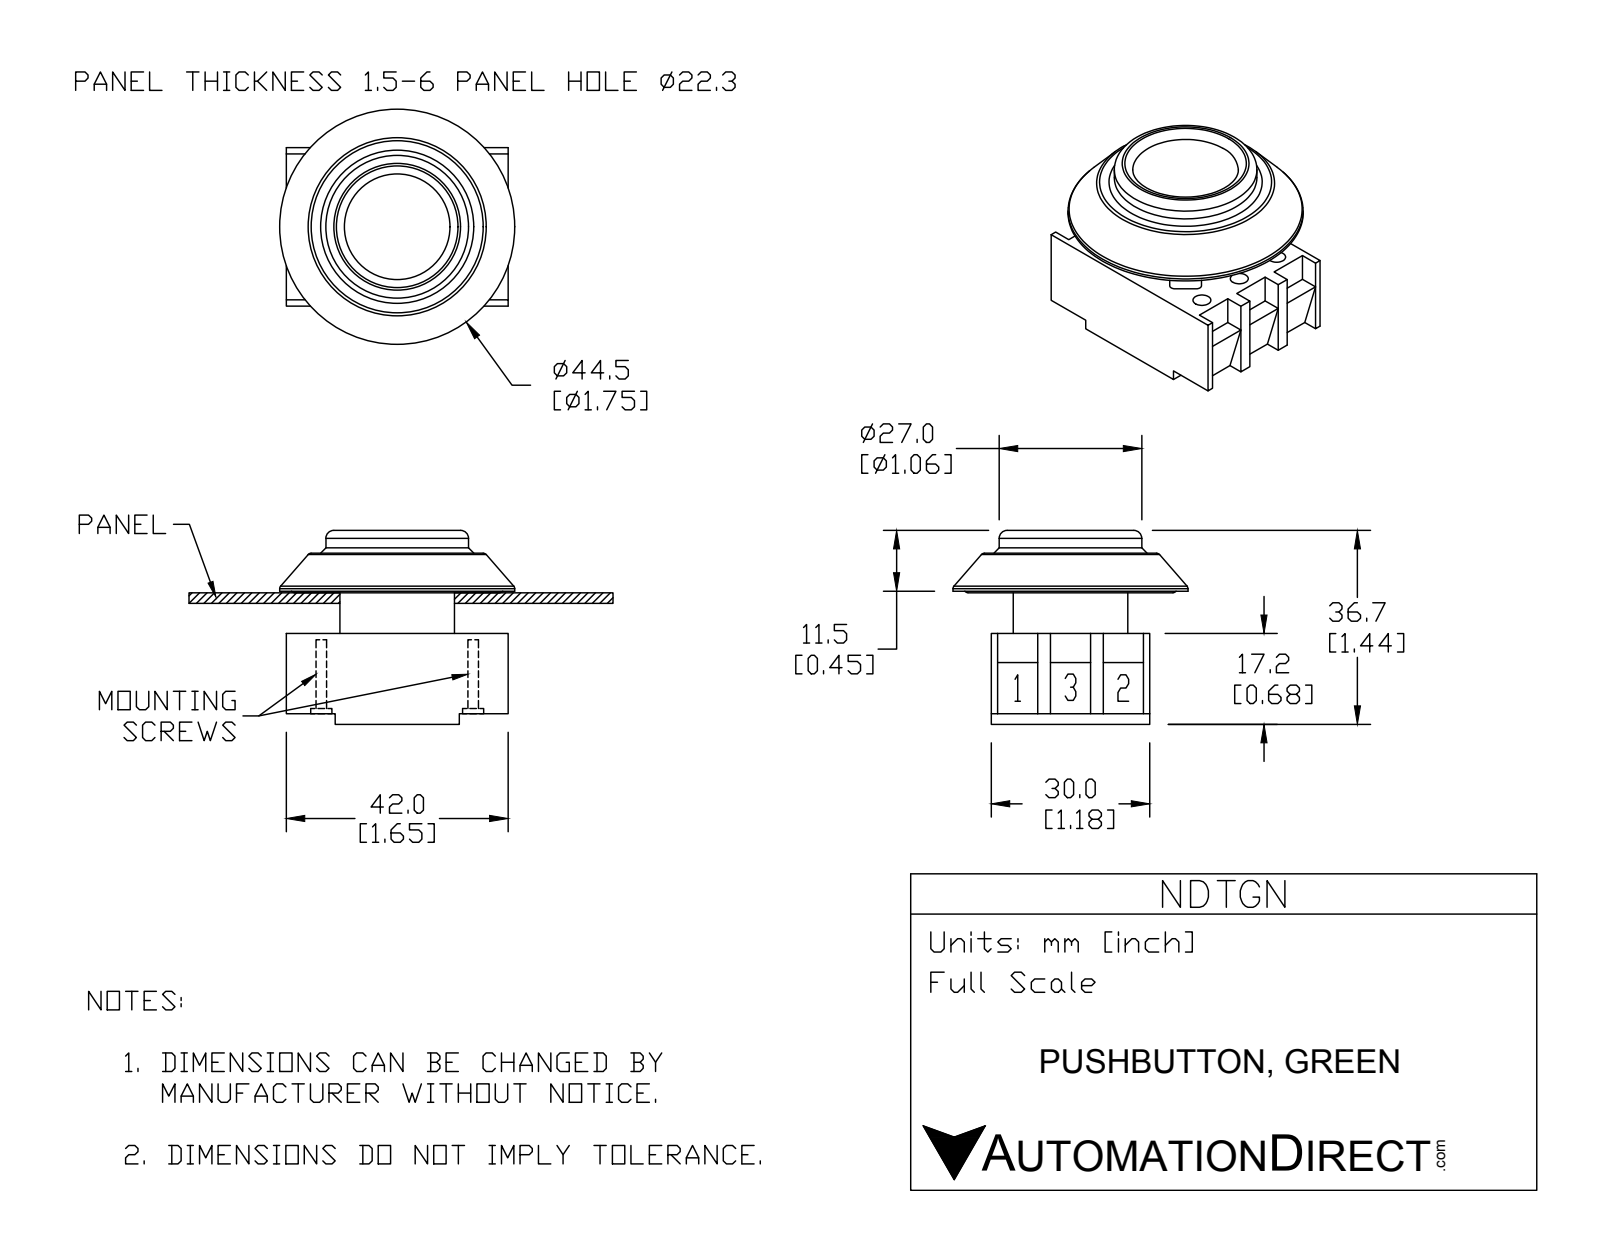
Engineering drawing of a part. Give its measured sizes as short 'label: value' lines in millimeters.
name: NDTGN
written by: SolidWorks 2015 (AUTOMOTIVE_DESIGN)
unit: mm
bodies: 7 solids, 217 faces (127 planar, 65 cylindrical, 25 other)
size: 44.5 × 44.5 × 36.7
volume: 25 120 mm³; area: 16 719 mm²
holes: 6× ⌀3.4, 6× ⌀5, 1× ⌀12.5
bosses: 2× ⌀4.6, 2× ⌀4, 1× ⌀44.5, 1× ⌀27, 1× ⌀21.7
rounds: 8× R1, 5× R8.7, 1× R11
face distances: 7.2, 15.2, 30, 10, 8, 7.5, 7.7, 10.3, 18, 23.2
hole spacings: 10, 17.52, 30.45, 28.76, 14.38, 20, 35.03
